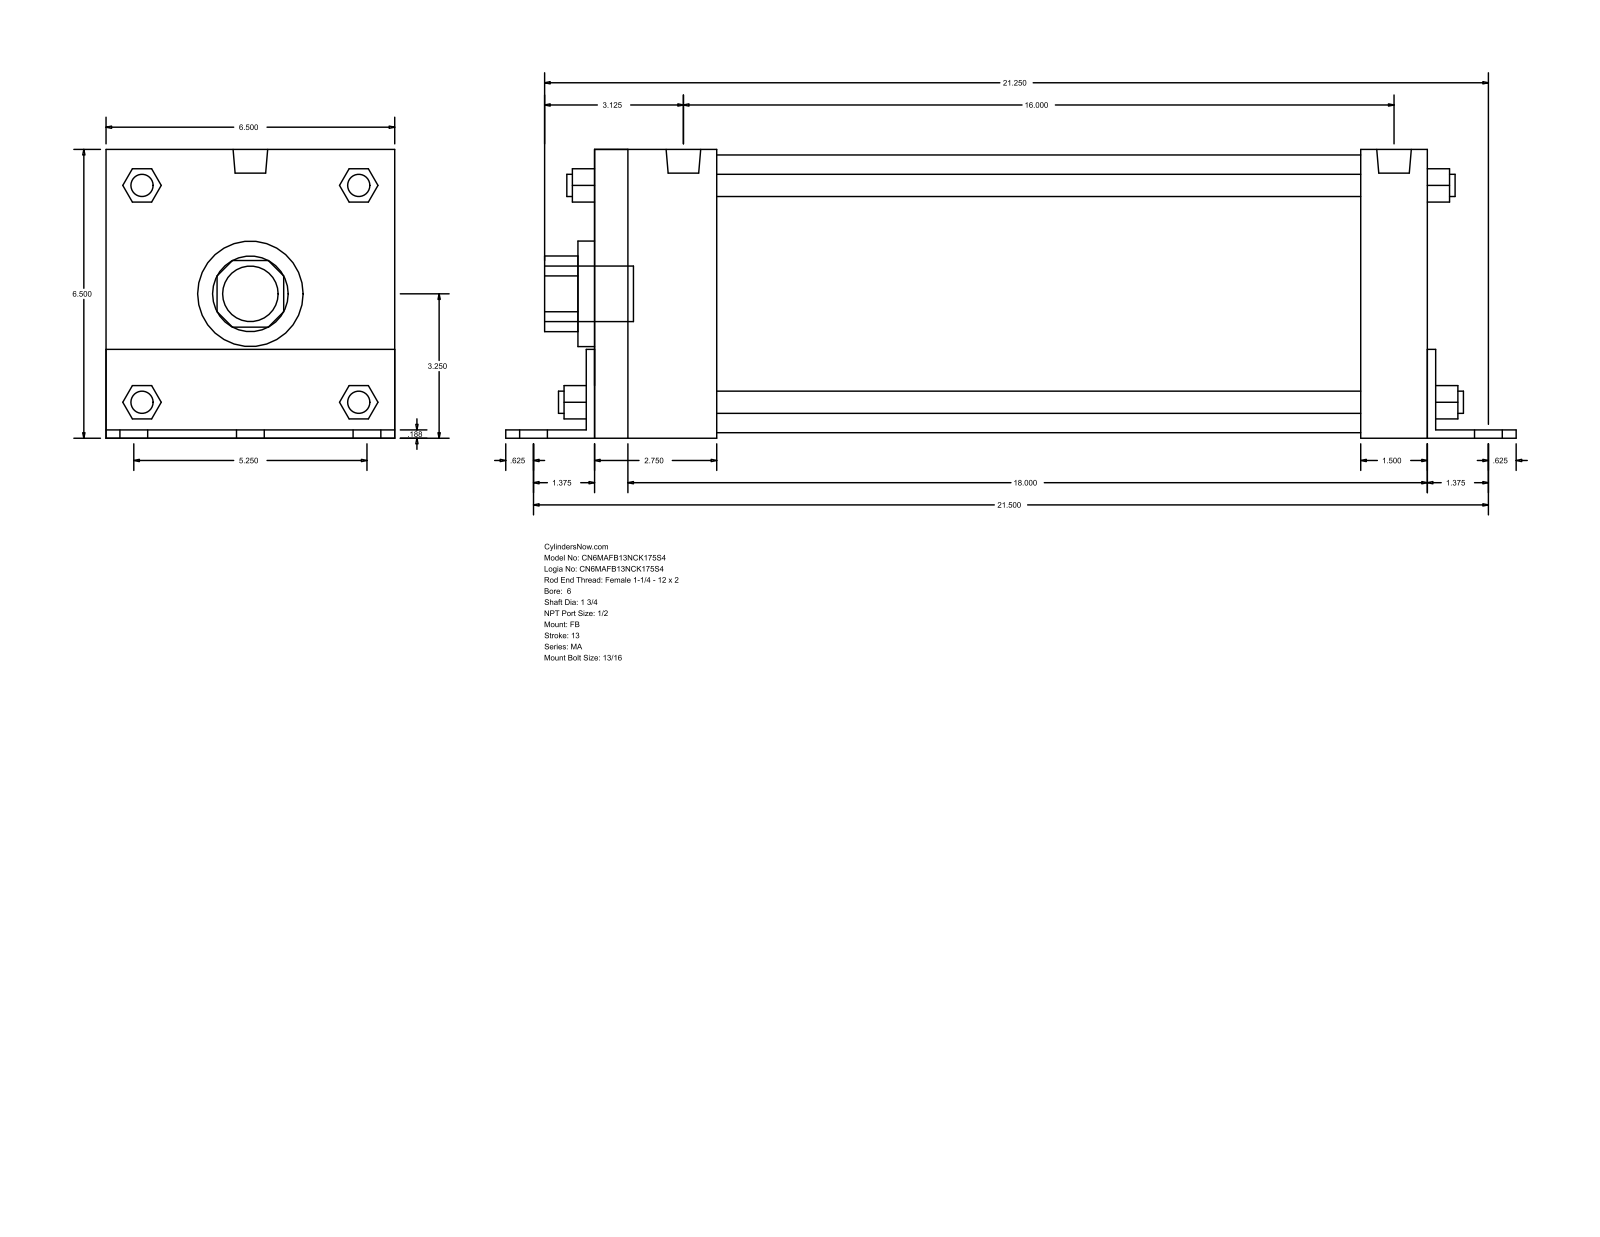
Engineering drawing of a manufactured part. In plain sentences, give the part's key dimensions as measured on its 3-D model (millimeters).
The part is named "MA_FB__0600_1.75". Its 3-D file was written by "GSSL Pune (CONFIG_CONTROL_DESIGN)". It is 0 solids with 140 faces: 105 planar, 35 cylindrical and 0 other. Overall it measures 577.85 by 165.15 by 165.1 millimeters. Round holes: 1 of diameter 44.45, 1 of diameter 60.33, 1 of diameter 158.75. Round bosses or shafts: 6 of diameter 20.64, 4 of diameter 17.46, 4 of diameter 12.7, 2 of diameter 19.77, 1 of diameter 31.75. Partial cylindrical surfaces (rounded edges, fillets, slot ends): 1 of radius 21.63, 1 of radius 32.05. The main face-to-face distances are 165.1, 4.76, 476.25, 165.15, 4.71, 160.39, 4.77, 42.86, 481.02, 481.01.
